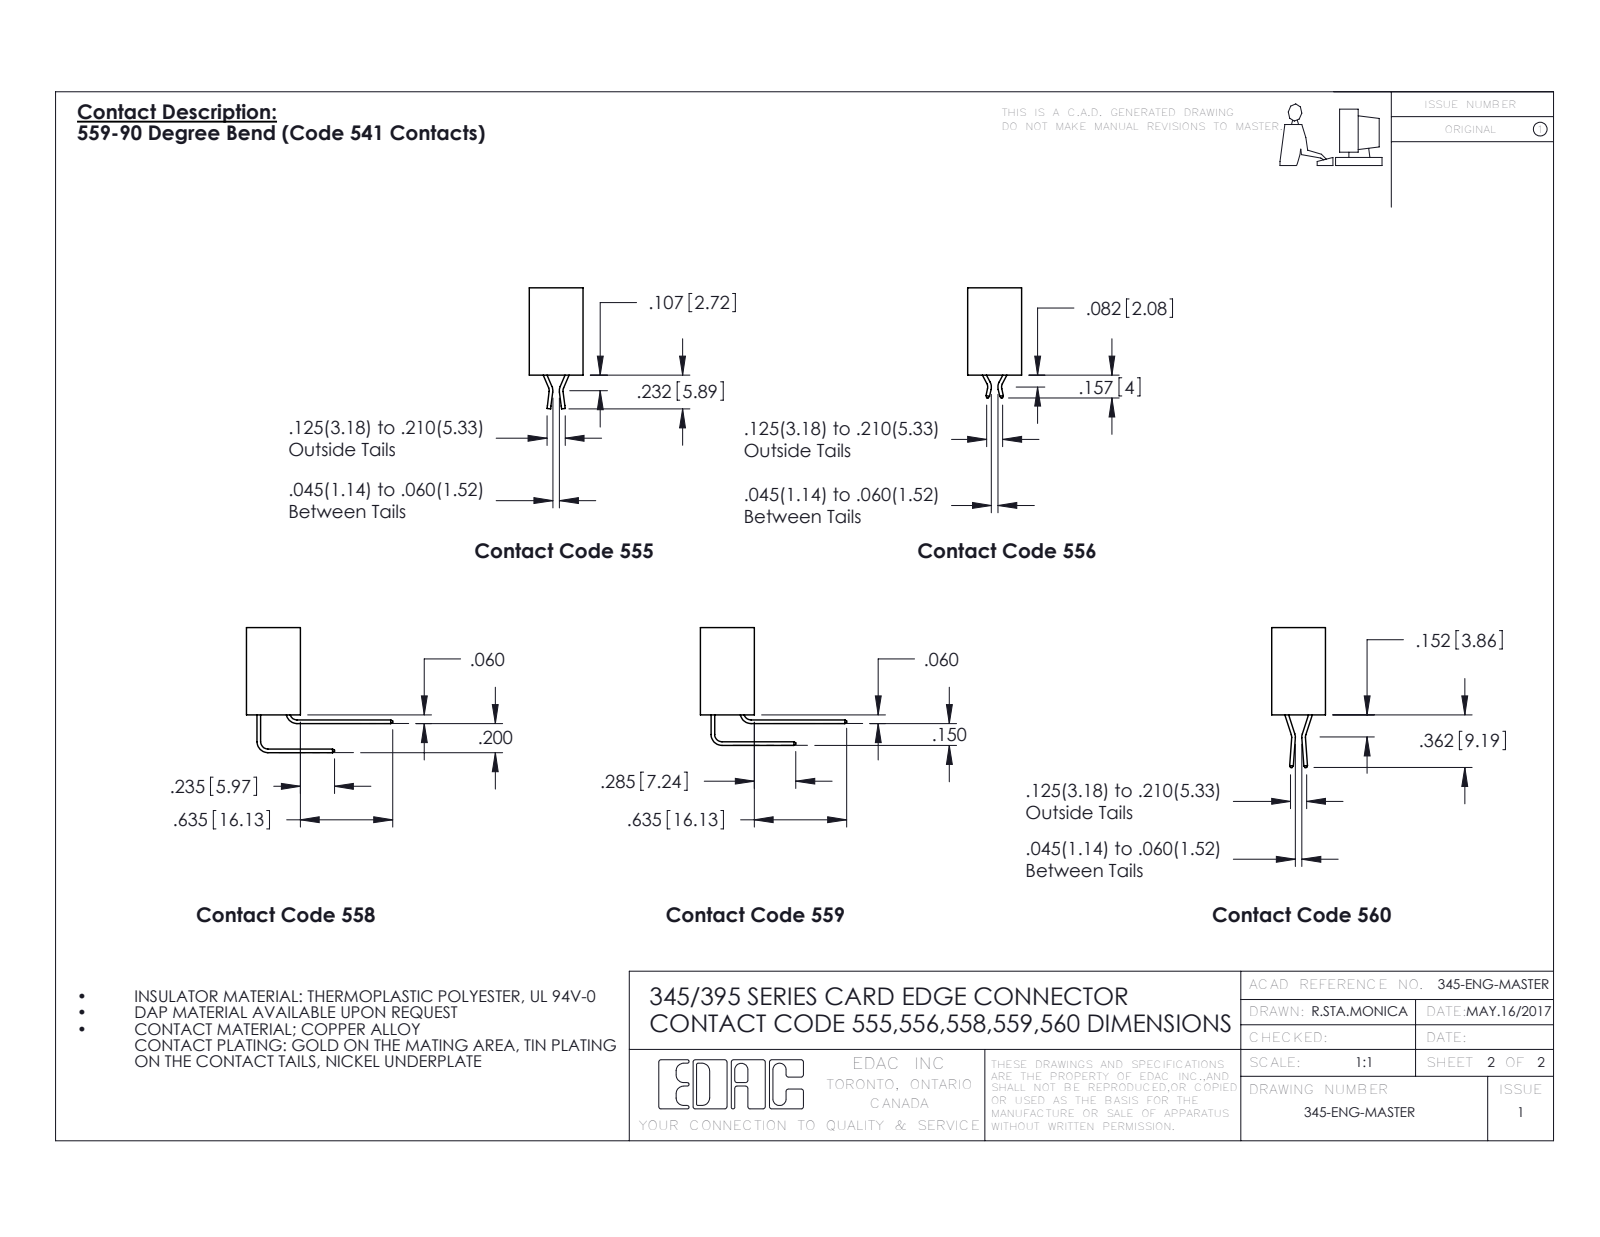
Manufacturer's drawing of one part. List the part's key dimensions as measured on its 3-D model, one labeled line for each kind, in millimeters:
Part name (STEP PRODUCT): 345-292-001_558 559 Tail - 1; 395-016-559-112; 345 Part_Flush Mounting Lugs - Side Mount
STEP written by: SolidWorks 2016 (CONFIG_CONTROL_DESIGN)
Units: millimetres
Bodies: 17 solids, 1086 faces (752 planar, 334 cylindrical, 0 other)
Overall size (bounding box): 61.8 × 25.5 × 16.7
Volume: 5 620 mm³ · Surface area: 7 297 mm²
Round holes (diameter × count): ⌀3.3 ×2, ⌀1.6 ×1
Partial cylindrical surfaces — rounded edges, fillets, slot ends (radius × count): R0.2 ×32, R0.3 ×22, R0.2 ×6, R0.8 ×6, R0.7 ×3, R0.8 ×2, R1 ×2, R0.4 ×1
Main face-to-face distances: 7.6, 1.8, 5.1, 9.4, 2.5, 6.9, 0.6, 5.7, 2.5, 1.3
Hole centre spacings: 55.2
